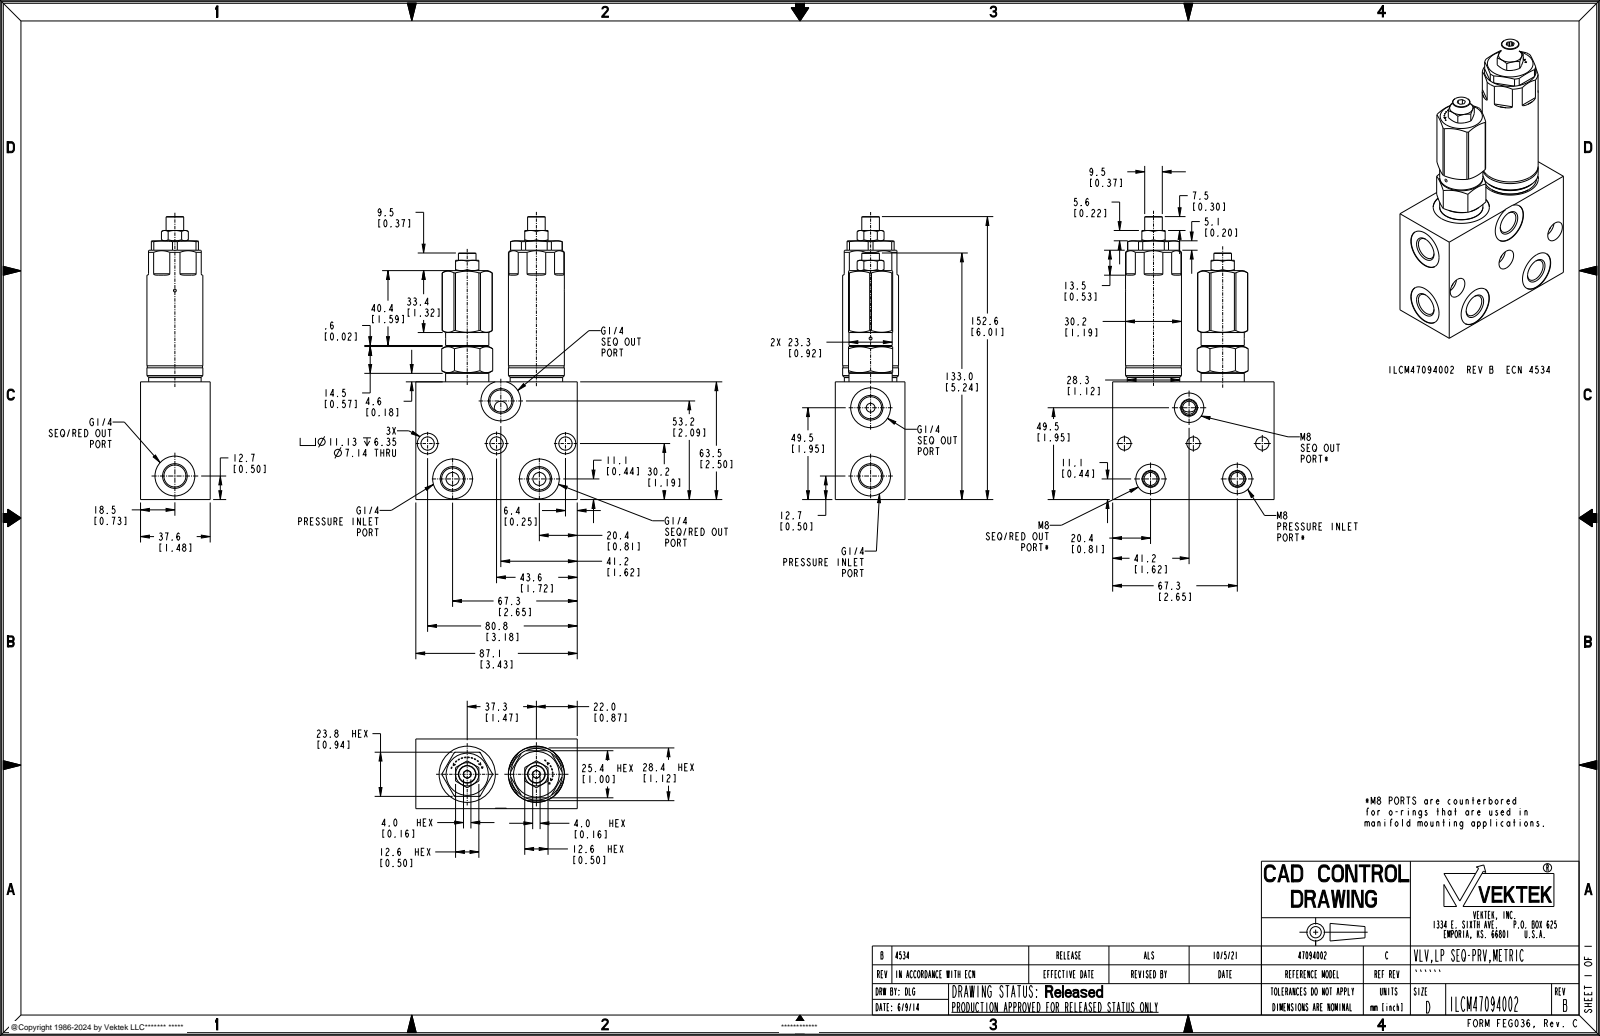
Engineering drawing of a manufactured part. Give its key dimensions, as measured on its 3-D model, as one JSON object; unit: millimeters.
{"part_name": "ILCM47094002", "step_written_by": "PRO/ENGINEER BY PARAMETRIC TECHNOLOGY CORPORATION, 2013320 (CONFIG_CONTROL_DESIGN)", "units": "millimeters", "bodies": {"solids": 1, "faces": 316, "planar": 104, "cylindrical": 131, "other": 81}, "overall_size": [157.56, 87.12, 37.59], "volume_mm3": 266876, "surface_area_mm2": 50741, "round_holes": [[11.89, 5], [21.49, 5], [7.01, 3], [7.14, 3], [11.13, 3], [15.88, 3], [2.39, 2], [9.96, 2], [30.3, 2], [1.57, 1], [4.75, 1], [5.16, 1]], "round_bosses_or_shafts": [[9.53, 2], [30.18, 1], [28.32, 1], [23.32, 1], [20.32, 1], [17.4, 1], [17.02, 1], [15.8, 1]], "partial_cylinders_radius": [[10.87, 1], [14.29, 1]], "face_to_face_distances": [37.59, 63.5, 87.12, 23.82, 39.65, 23.83, 37.34, 86.87, 71.3, 15.82], "hole_center_spacings": [37.21, 1.27, 3.66, 18.17, 18.29, 19.44, 23.08, 23.38]}
